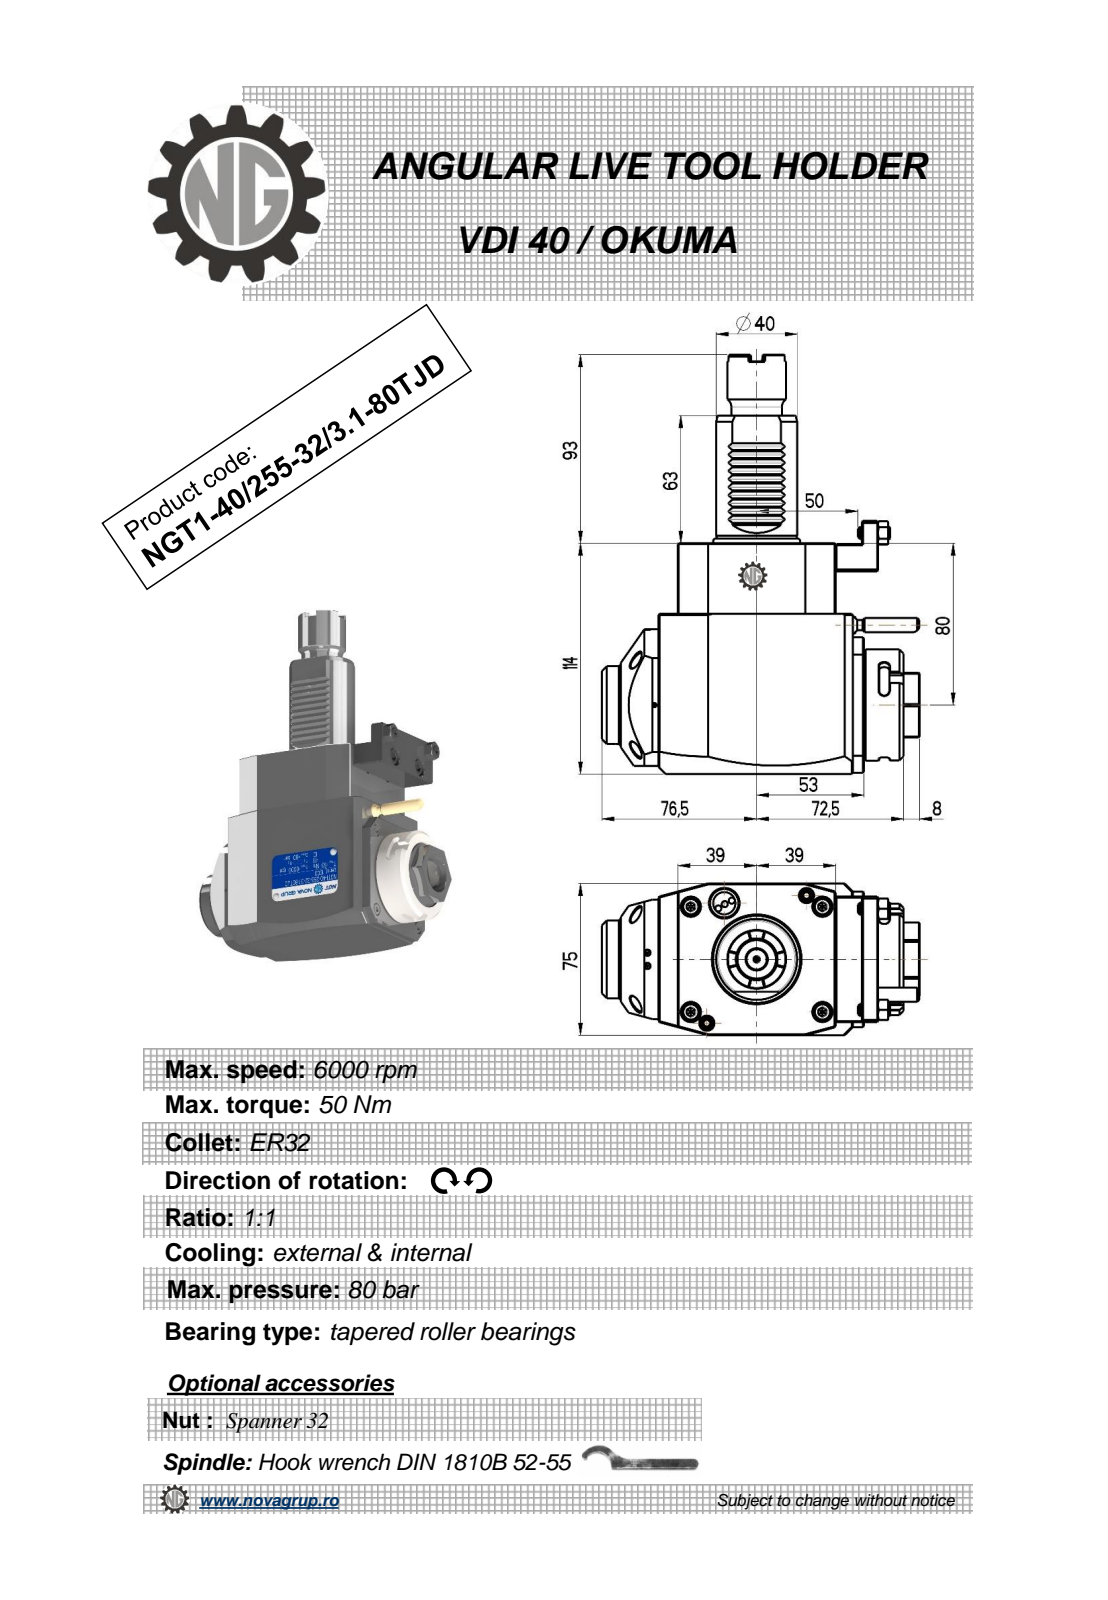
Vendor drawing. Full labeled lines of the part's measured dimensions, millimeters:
Part name (STEP PRODUCT): NGT1_40_255_32_3_1_80TJD
STEP written by: PRO/ENGINEER BY PARAMETRIC TECHNOLOGY CORPORATION, 2010280 (CONFIG_CONTROL_DESIGN)
Units: millimetres
Bodies: 1 solid, 402 faces (200 planar, 72 cylindrical, 130 other)
Overall size (bounding box): 207 × 157 × 75
Volume: 1 006 000 mm³ · Surface area: 77 210 mm²
Round holes (diameter × count): ⌀2.5 ×1, ⌀3 ×1, ⌀23 ×1
Round bosses / shafts (diameter × count): ⌀6 ×2, ⌀55 ×1, ⌀48 ×1, ⌀40 ×1, ⌀38.5 ×1, ⌀29 ×1, ⌀25 ×1, ⌀8.96 ×1
Partial cylindrical surfaces — rounded edges, fillets, slot ends (radius × count): R0.3 ×10, R0.31 ×10, R2.5 ×6, R180 ×2, R0.5 ×1, R10 ×1, R24.5 ×1, R37.5 ×1
Main face-to-face distances: 75, 114, 14, 21, 92, 12.5, 0.5, 111.5, 19.5, 7
Hole centre spacings: 43.2
